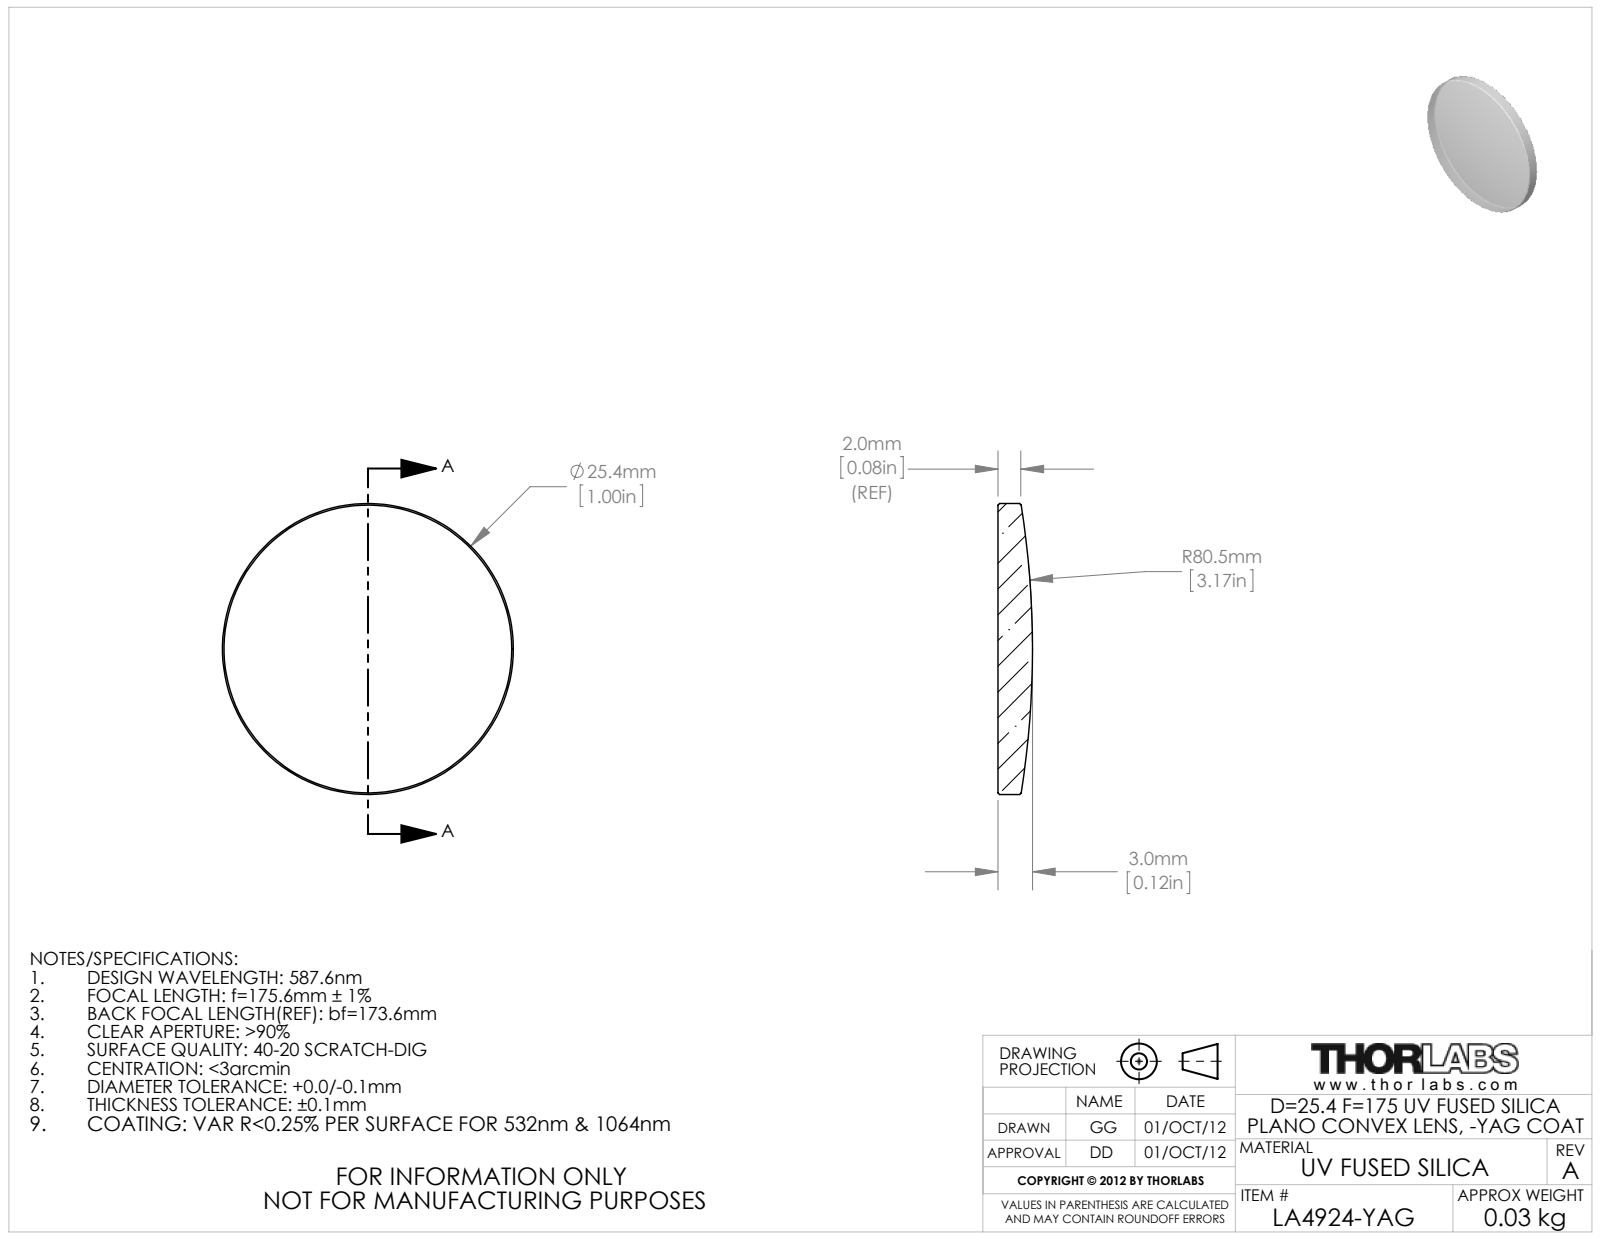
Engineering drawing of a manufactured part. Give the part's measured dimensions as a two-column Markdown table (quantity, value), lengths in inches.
| quantity | value |
| --- | --- |
| part name | 24955-E0W |
| STEP written by | SolidWorks 2011 (CONFIG_CONTROL_DESIGN) |
| units | inches |
| bodies | 1 solid, 9 faces (1 planar, 2 cylindrical, 6 other) |
| overall size | 1 × 1 × 0.119 |
| volume | 0.077 in³ |
| surface area | 1.806 in² |
| round bosses / shafts (diameter × count) | 1 × 1 |
